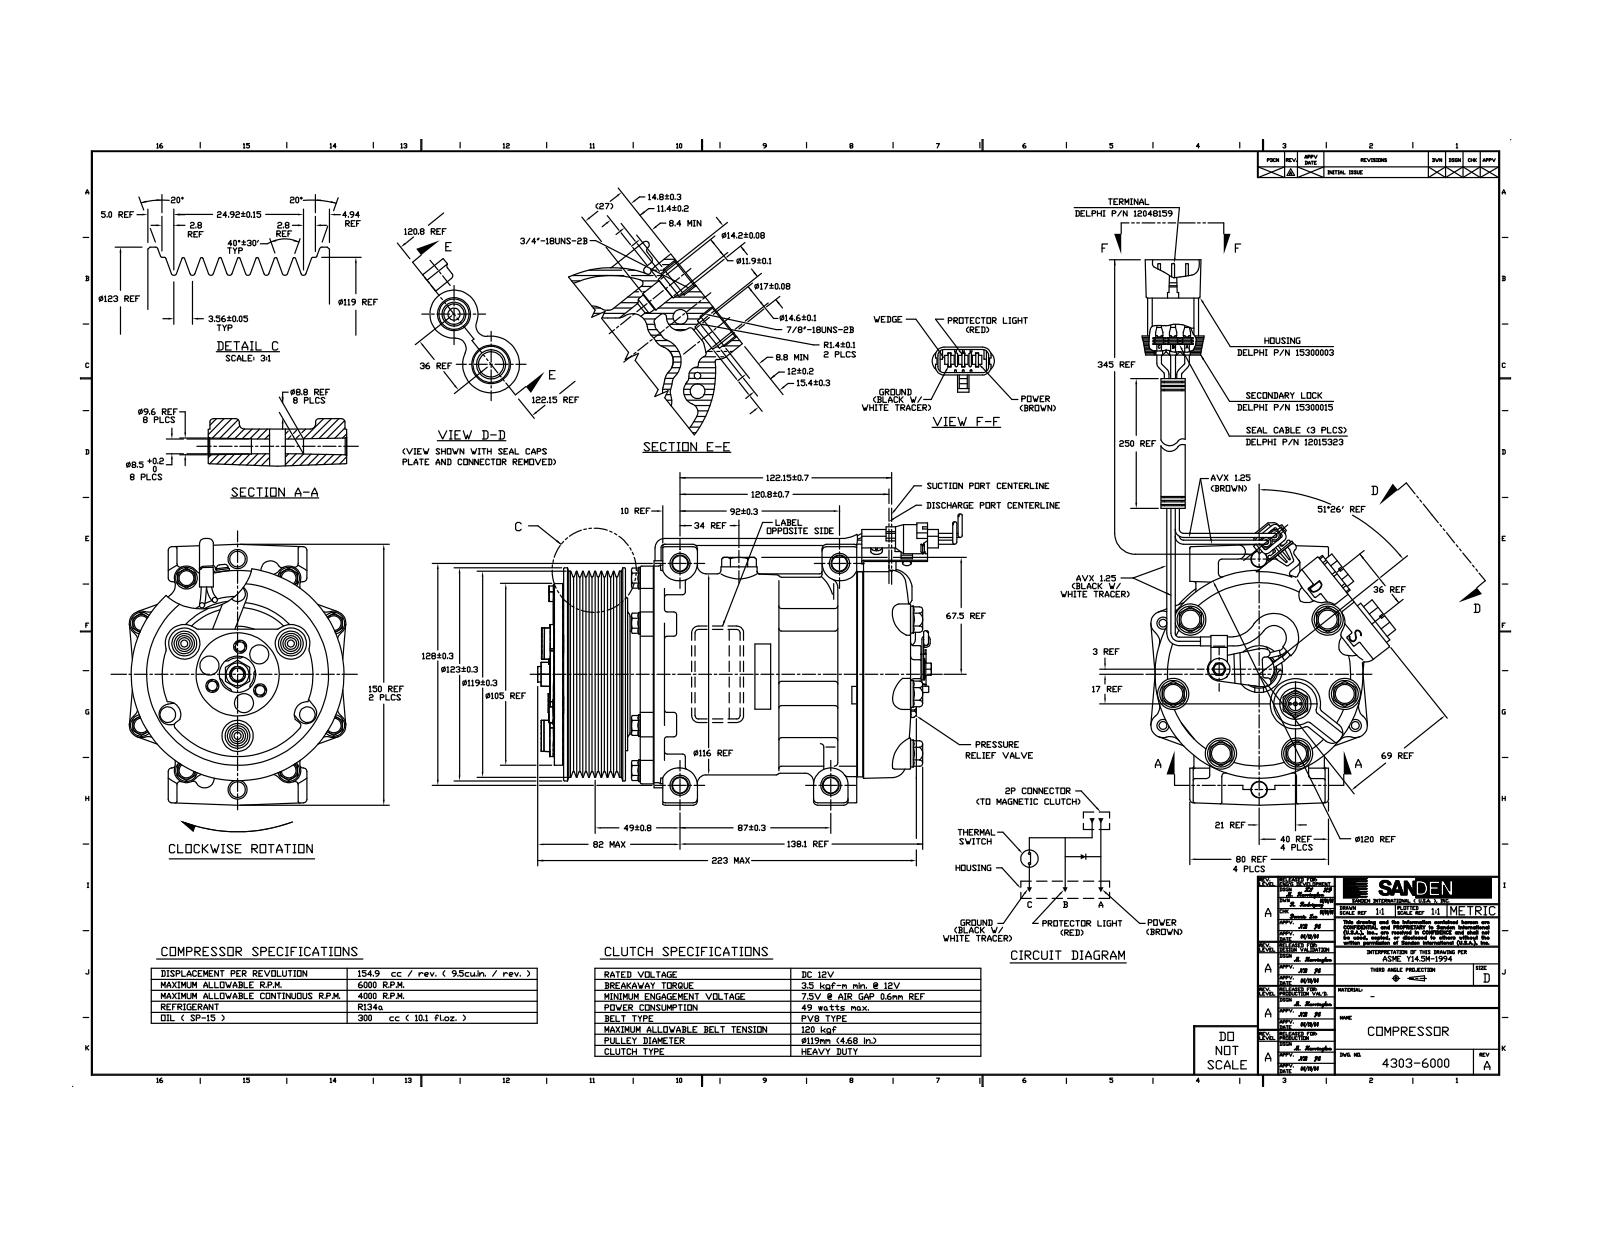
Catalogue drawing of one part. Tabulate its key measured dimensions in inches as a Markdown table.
| quantity | value |
| --- | --- |
| part name | SANDEN_4303_REV_B_COMPR_AC |
| STEP written by | SolidWorks 2010 (CONFIG_CONTROL_DESIGN) |
| units | inches |
| bodies | 1 solid, 1726 faces (636 planar, 704 cylindrical, 386 other) |
| overall size | 19.262 × 9.449 × 5.626 |
| volume | 139.5 in³ |
| surface area | 369.5 in² |
| round holes (diameter × count) | 0.315 × 6, 0.335 × 4, 0.201 × 3, 0.25 × 3, 0.295 × 3, 0.354 × 2, 0.827 × 2, 0.157 × 1, 0.469 × 1, 0.508 × 1, 0.575 × 1, 0.689 × 1 |
| round bosses / shafts (diameter × count) | 0.106 × 25, 0.709 × 9, 0.492 × 8, 0.63 × 3, 0.433 × 3, 0.354 × 3, 0.268 × 3, 0.197 × 3 |
| partial cylindrical surfaces (radius × count) | 0.276 × 39, 0.079 × 33, 0.02 × 31, 0.197 × 26, 0.039 × 22, 0.059 × 12, 0.157 × 10, 0.177 × 10 |
| main face-to-face distances | 1.752, 0.354, 0.165, 1.398, 1.941, 1.587, 0.189, 1.776, 1.421, 0.024 |
| hole center spacings | 1.657, 0.63, 1.091, 1.154, 1.205, 1.831, 2.026, 2.254 |
